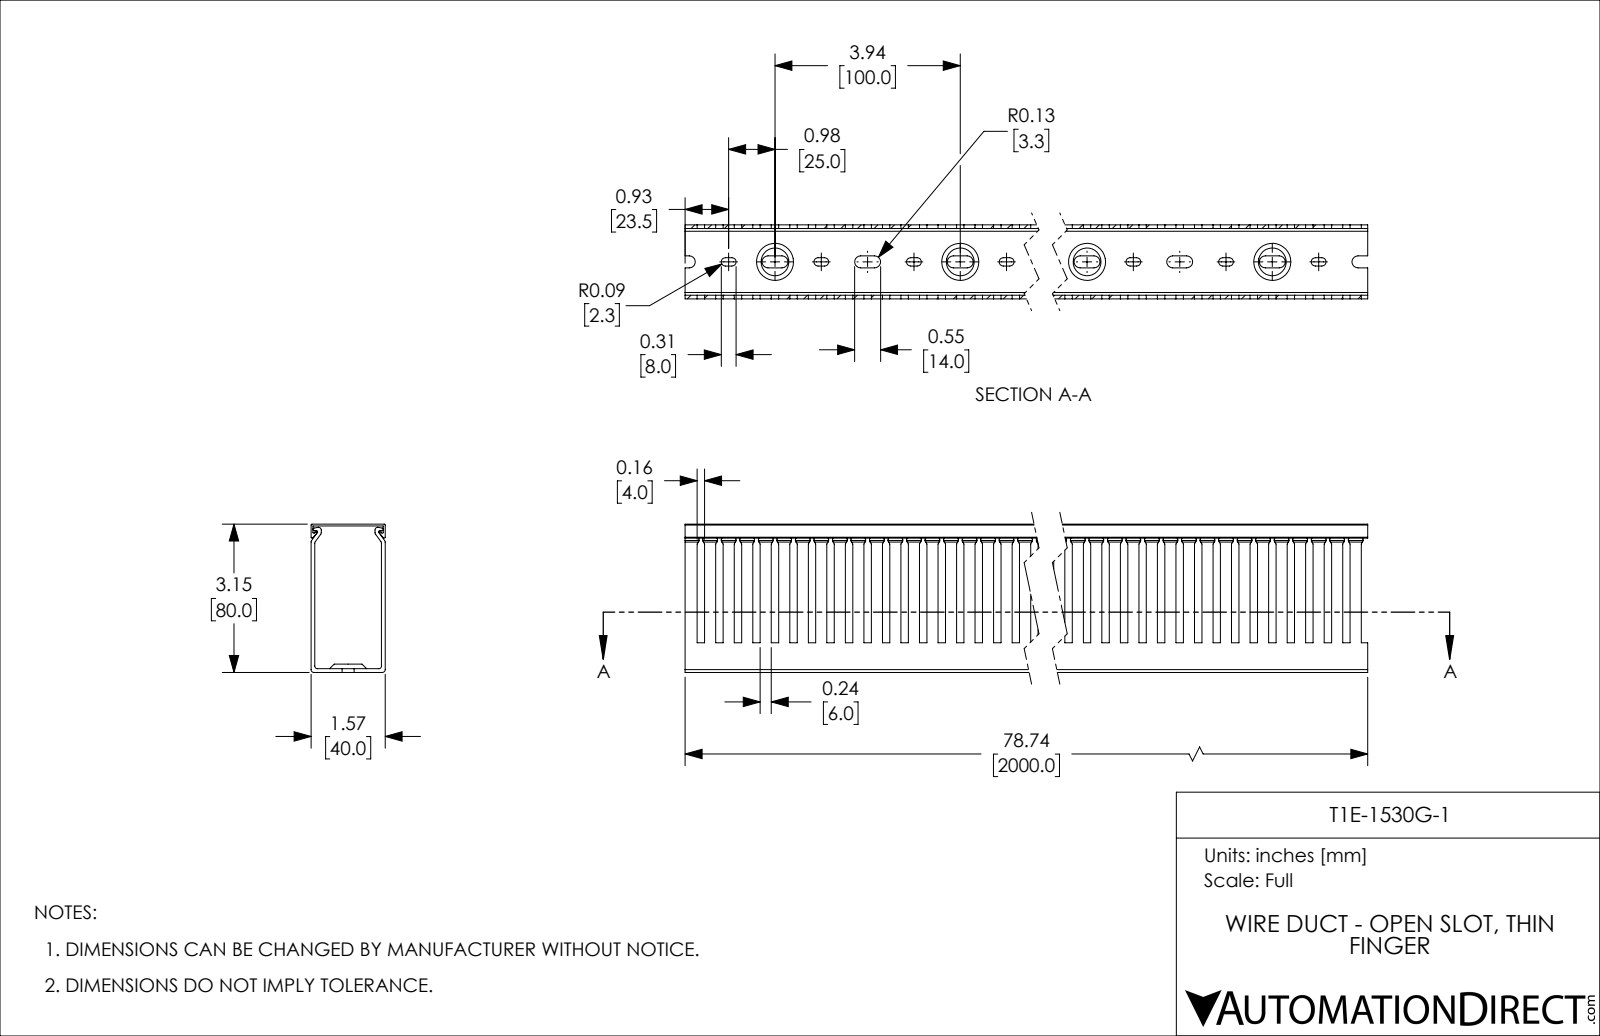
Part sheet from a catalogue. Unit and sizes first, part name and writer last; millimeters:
Units: millimetres
Overall size (bounding box): 2000 × 80 × 40
Partial cylindrical surfaces — rounded edges, fillets, slot ends (radius × count): R2.25 ×80, R3.25 ×80, R1.5 ×12, R0.5 ×8, R0.75 ×6
Main face-to-face distances: 2, 38, 40, 36, 1, 80, 79, 77, 78, 39
Volume: 899 540 mm³ · Surface area: 1 017 000 mm²
Bodies: 2 solids, 1005 faces (534 planar, 431 cylindrical, 40 other)
Part name (STEP PRODUCT): T1E-1530G-1
STEP written by: SolidWorks 2021 (CONFIG_CONTROL_DESIGN)
